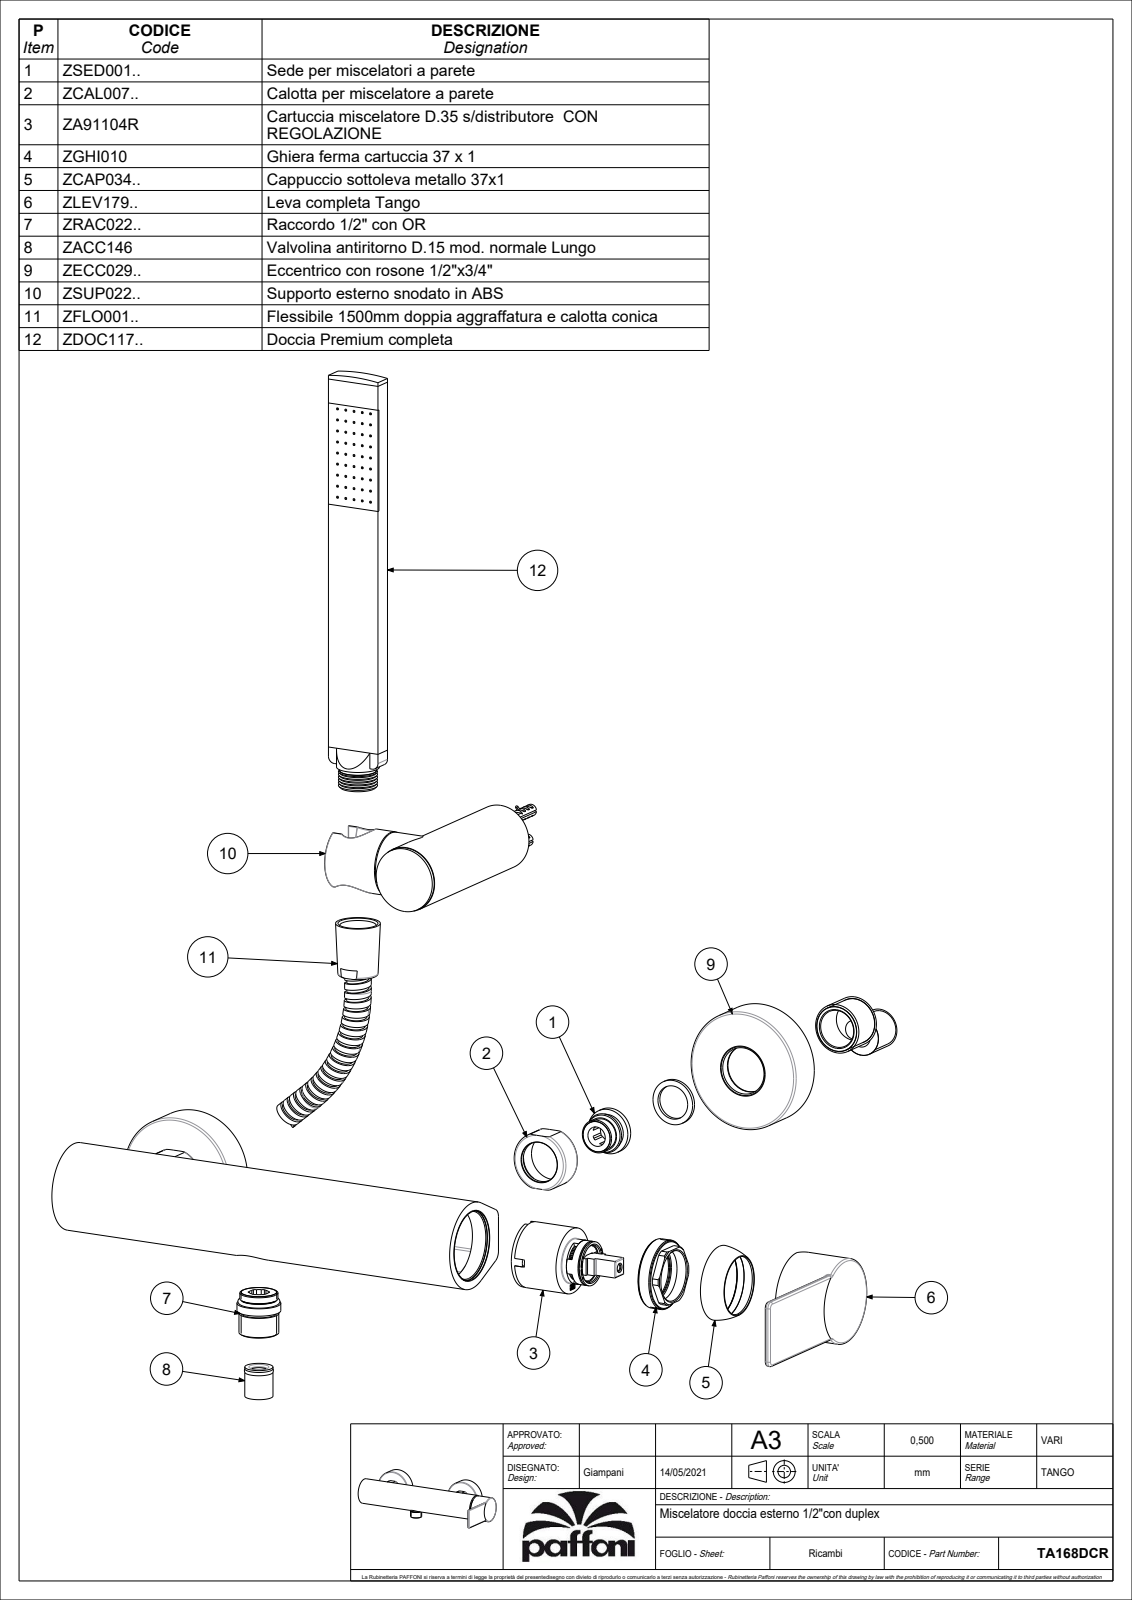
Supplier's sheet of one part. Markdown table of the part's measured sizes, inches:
| quantity | value |
| --- | --- |
| part name | TA168D |
| STEP written by | CREO PARAMETRIC BY PTC INC, 2020044 (CONFIG_CONTROL_DESIGN) |
| units | inches |
| bodies | 0 solids, 204 faces (61 planar, 46 cylindrical, 97 other) |
| overall size | 16.809 × 14.679 × 5.63 |
| round bosses / shafts (diameter × count) | 2.5 × 2, 1.791 × 1, 1.358 × 1, 1.339 × 1, 1.331 × 1, 1.319 × 1, 0.906 × 1, 0.886 × 1 |
| partial cylindrical surfaces (radius × count) | 0.012 × 6, 0.039 × 6, 0.059 × 2, 0.118 × 2, 0.138 × 2, 0.197 × 2, 0.614 × 2, 0.915 × 1 |
| main face-to-face distances | 2.776, 3.169, 0.394, 0.787, 1.988, 2.382, 1.378, 1.398, 0.591, 1.791 |
